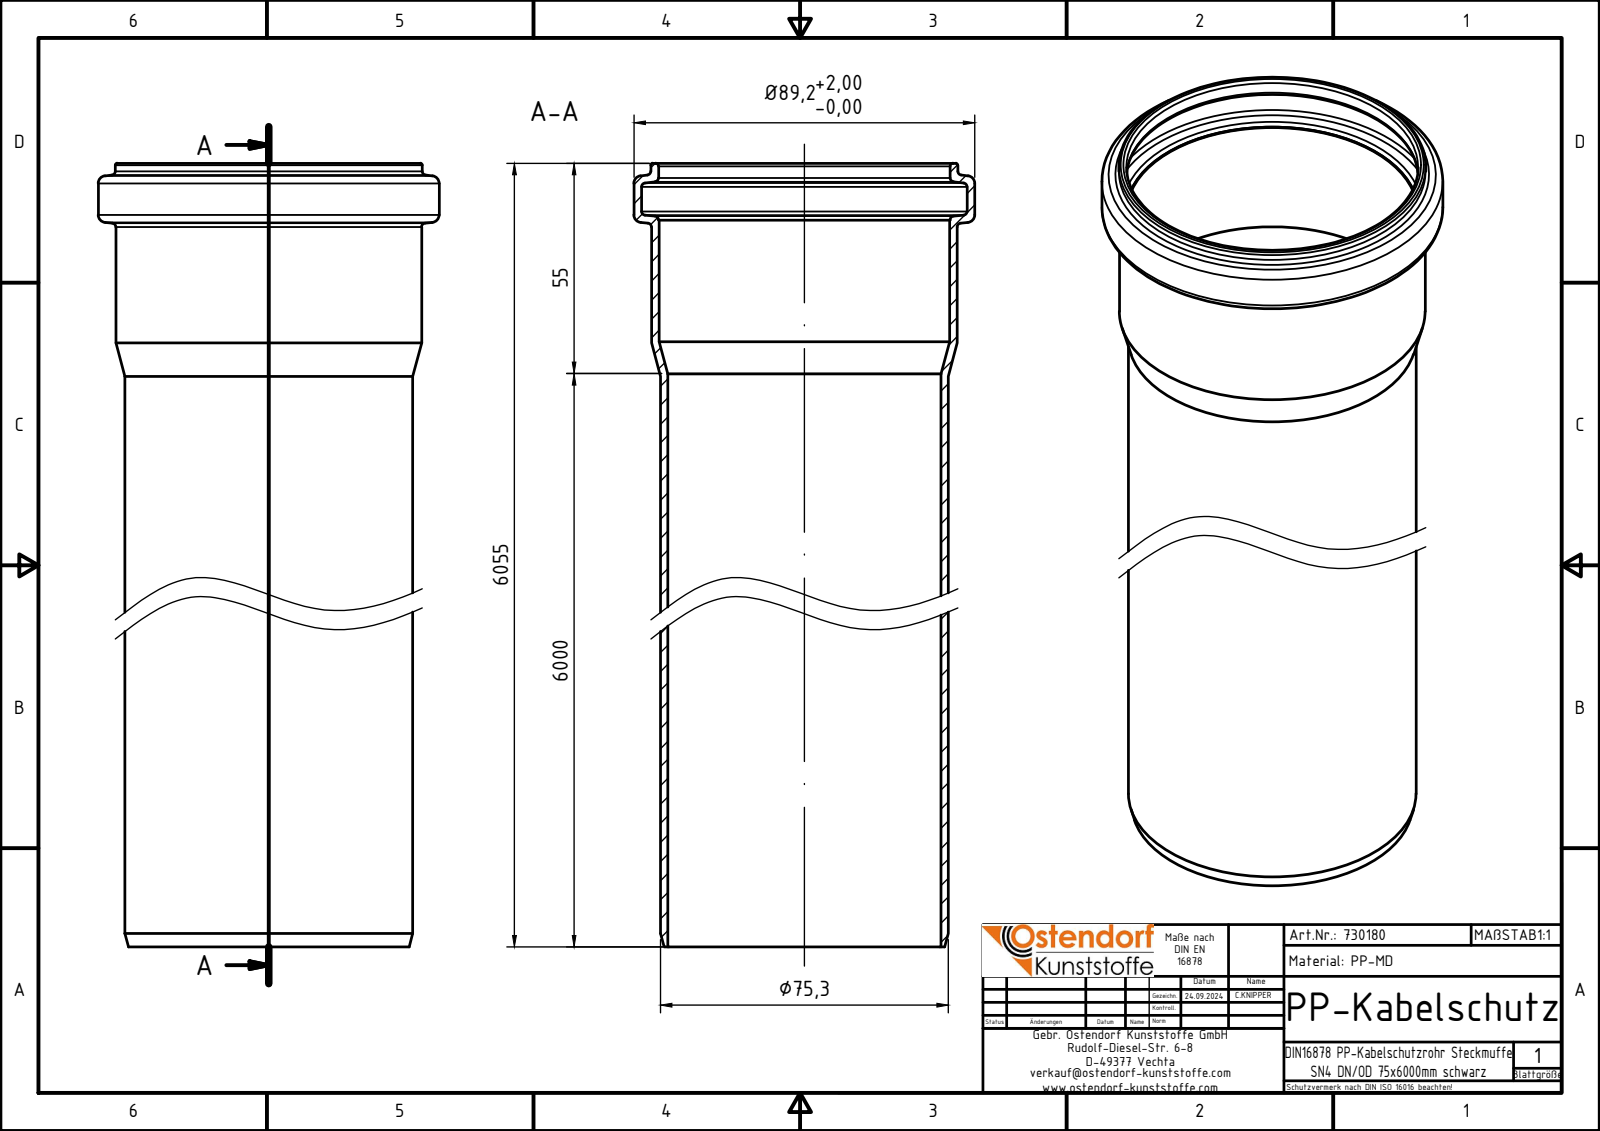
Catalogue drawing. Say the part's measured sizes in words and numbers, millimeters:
The part is named "730180z". Its 3-D file was written by "Autodesk Inventor 2024 (AUTOMOTIVE_DESIGN)". It is 1 solid with 29 faces: 3 planar, 9 cylindrical and 17 other. Overall it measures 6055 by 89.2 by 89.2 millimeters. Its volume is 2 660 000 cubic millimeters and its surface area 2 799 000 square millimeters. Round holes: 1 of diameter 71.5, 1 of diameter 76, 1 of diameter 76.3, 1 of diameter 85.2. Round bosses or shafts: 1 of diameter 89.2, 1 of diameter 80.3, 1 of diameter 80, 1 of diameter 75.3. The main face-to-face distances are 6055, 6040.11, 14.89.
